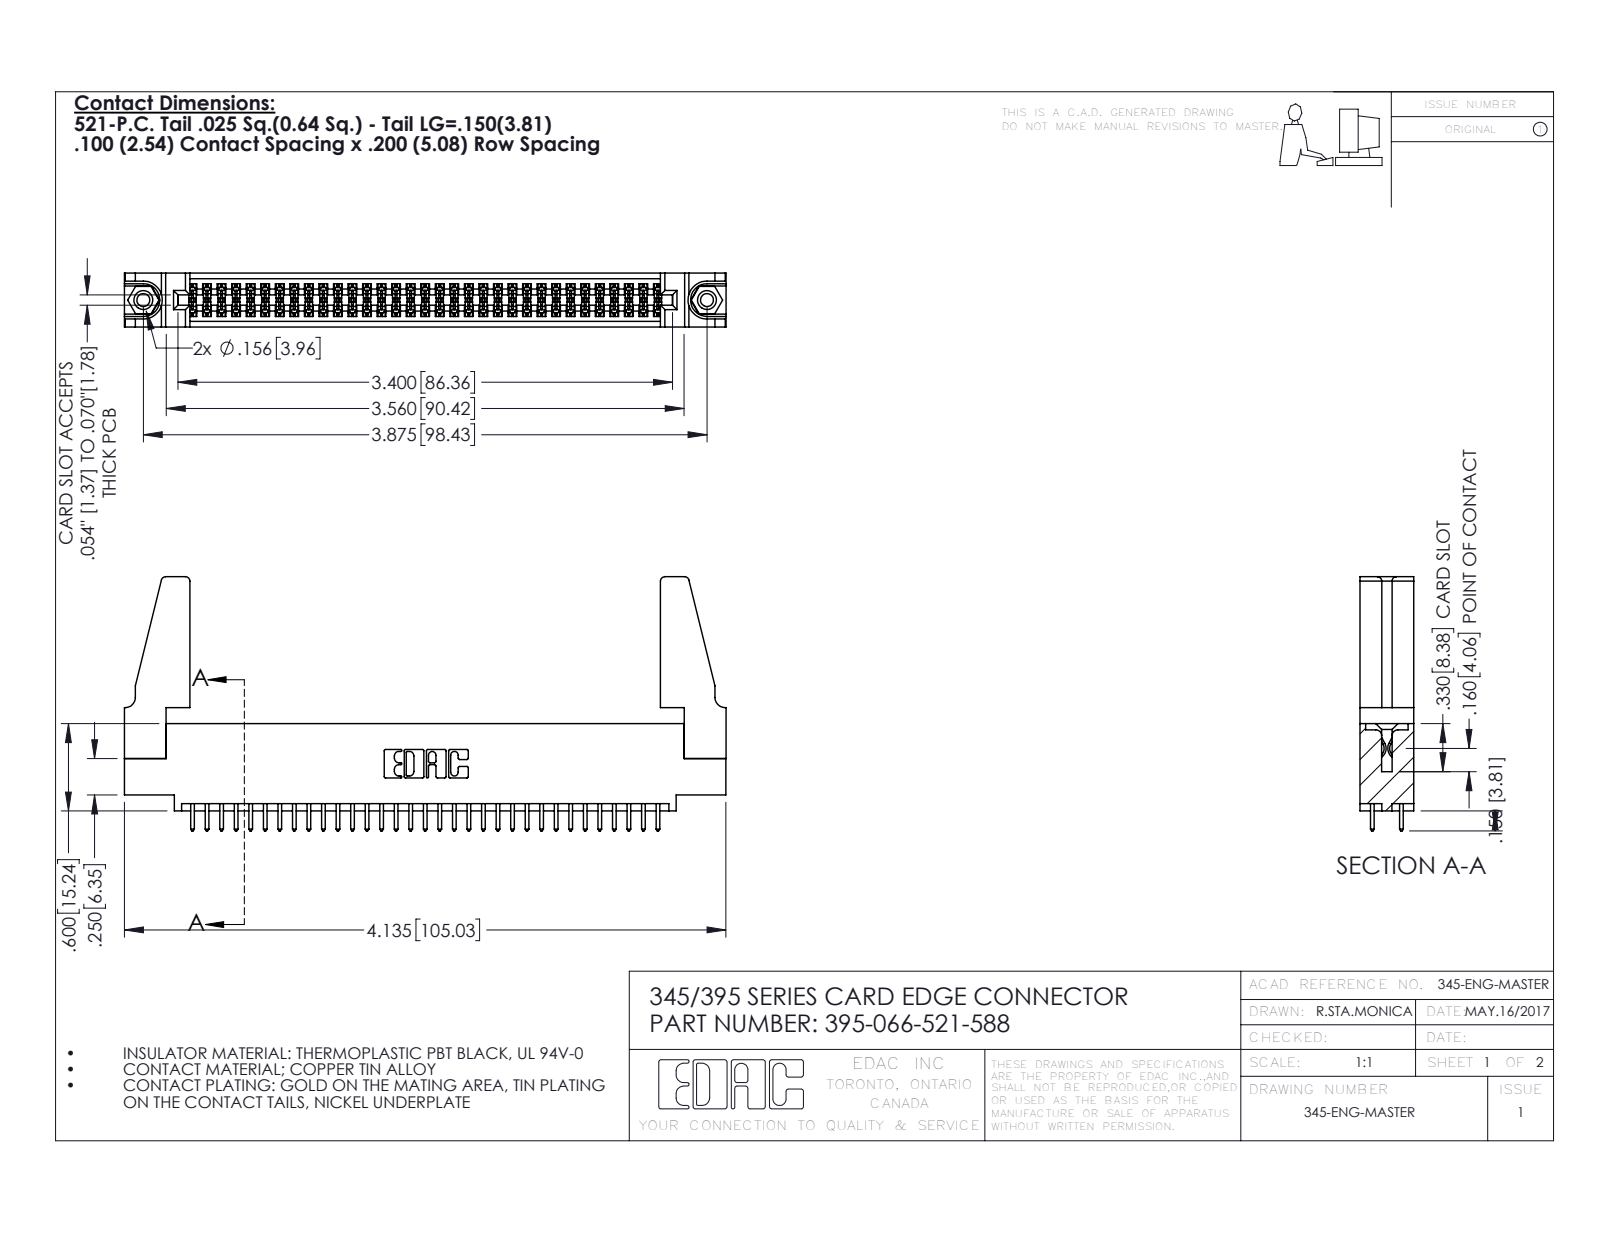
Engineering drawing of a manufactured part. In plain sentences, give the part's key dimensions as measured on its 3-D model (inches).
The part is named "345 Part_0.110 Offset - 0.156 Dia-TH; 345-250-001_345-250-001-102; 345-292-001_345-293-121; 395-066-521-588 (+1 more)". Its 3-D file was written by "SolidWorks 2016 (CONFIG_CONTROL_DESIGN)". It is 71 solids with 3554 faces: 2334 planar, 1204 cylindrical and 16 other. Overall it measures 4.136 by 1.747 by 0.37 inches. Its volume is 0.81 cubic inches and its surface area 27.4 square inches. Round holes: 2 of diameter 0.089, 2 of diameter 0.125, 2 of diameter 0.156, 1 of diameter 0.064. Round bosses or shafts: 2 of diameter 0.155. Partial cylindrical surfaces (rounded edges, fillets, slot ends): 99 of radius 0.006, 66 of radius 0.01, 22 of radius 0.01, 8 of radius 0.03, 6 of radius 0.007, 6 of radius 0.031, 3 of radius 0.026, 2 of radius 0.014. The main face-to-face distances are 0.072, 0.298, 0.37, 0.2, 0.098, 0.272, 0.025, 0.225, 0.175, 0.149. The hole center spacings are 0.27, 3.64, 3.875.
